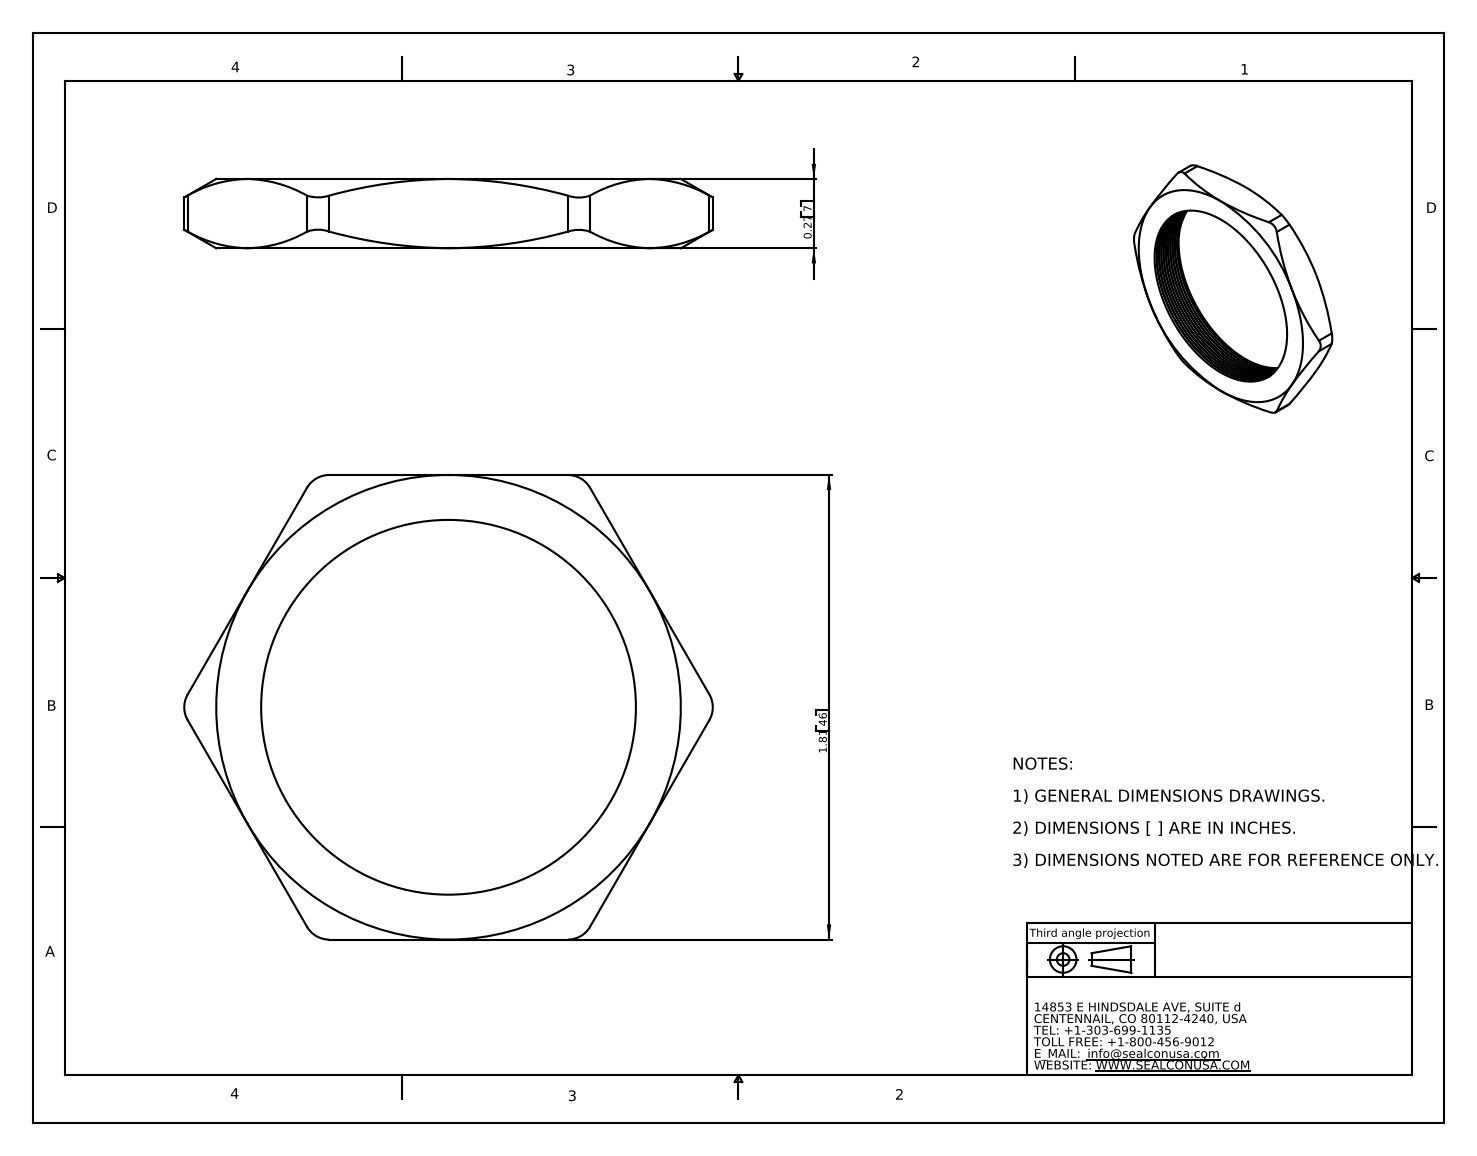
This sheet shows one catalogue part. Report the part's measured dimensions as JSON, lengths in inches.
{"part_name": "NP-29-GY", "step_written_by": "SolidWorks 2007 (CONFIG_CONTROL_DESIGN)", "units": "inches", "bodies": {"solids": 1, "faces": 93, "planar": 8, "cylindrical": 27, "other": 58}, "overall_size": [2.059, 1.81, 0.27], "volume_in3": 0.289, "surface_area_in2": 6.138, "round_holes": [[1.46, 1]], "partial_cylinders_radius": [[0.1, 6]], "face_to_face_distances": [0.27, 1.81]}
